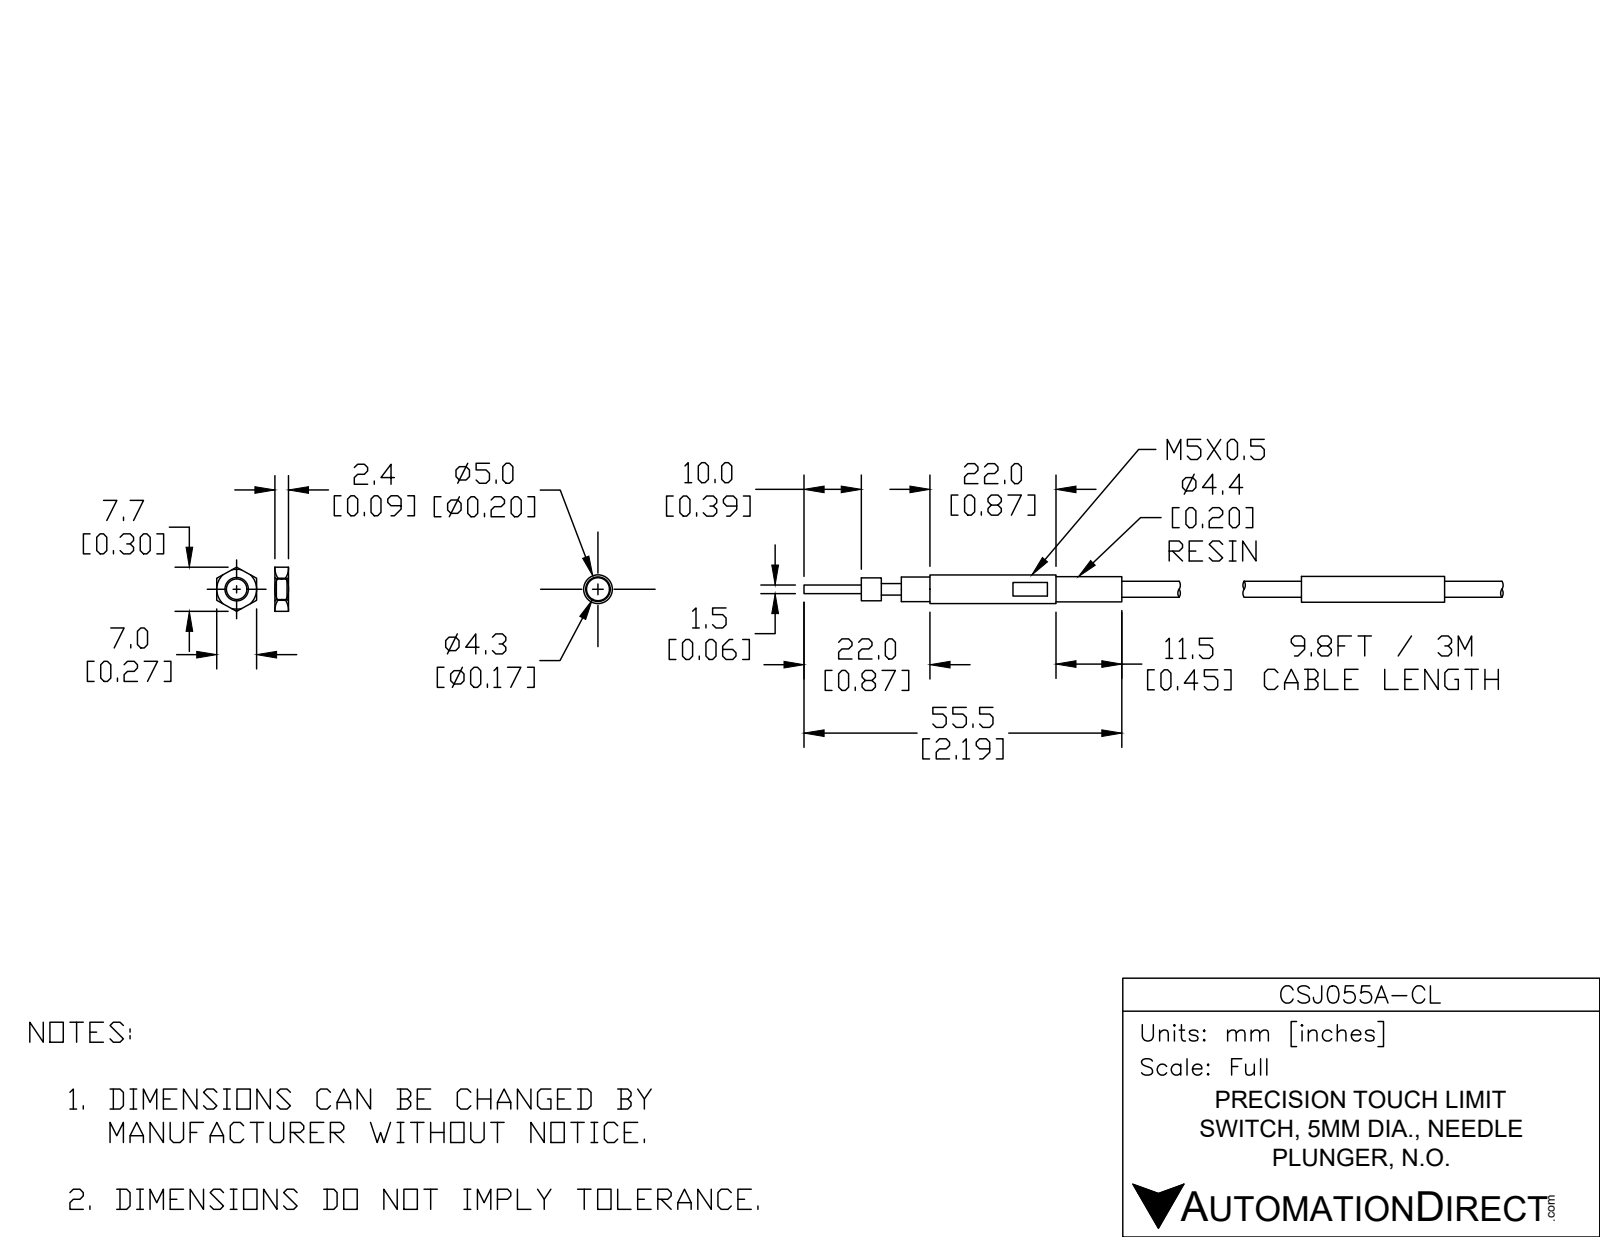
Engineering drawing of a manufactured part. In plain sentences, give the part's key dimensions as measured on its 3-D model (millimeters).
The part is named "CSJ055A-CL". Its 3-D file was written by "SolidWorks 2017 (AUTOMOTIVE_DESIGN)". It is 2 solids with 28 faces: 18 planar, 10 cylindrical and 0 other. Overall it measures 113.5 by 5.1 by 5.1 millimeters. Its volume is 1 300 cubic millimeters and its surface area 1 409 square millimeters. Round bosses or shafts: 1 of diameter 5.1, 1 of diameter 4.5, 1 of diameter 4.4, 1 of diameter 4.3, 1 of diameter 4, 1 of diameter 2.8, 1 of diameter 2, 1 of diameter 1.5. The main face-to-face distances are 3.5, 45.5, 4.4, 58, 10.5, 12.5, 22, 7, 23, 42.
